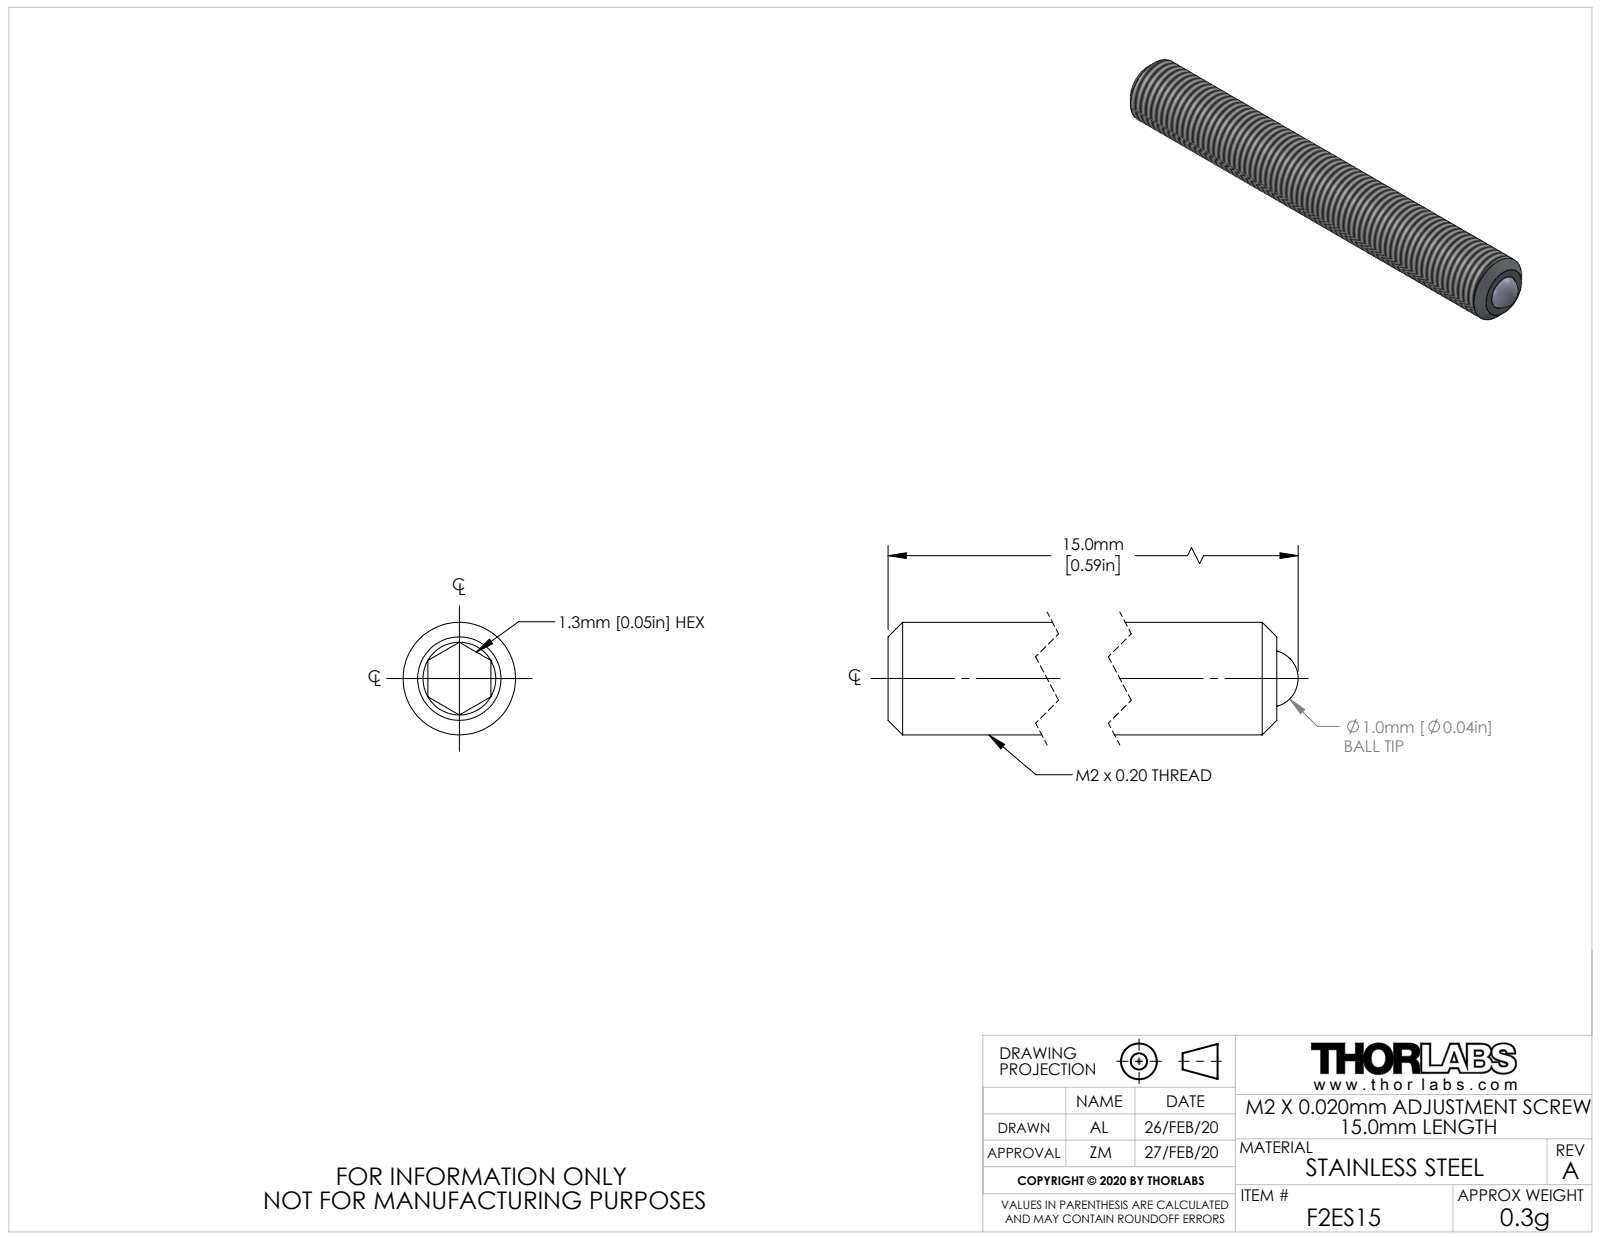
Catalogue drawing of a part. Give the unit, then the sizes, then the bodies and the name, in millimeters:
Units: millimetres
Overall size (bounding box): 15 × 2 × 2
Round holes (diameter × count): ⌀1 ×1
Round bosses / shafts (diameter × count): ⌀2 ×1
Main face-to-face distances: 1.1, 12.6, 2, 14.6
Volume: 50 mm³ · Surface area: 106 mm²
Bodies: 2 solids, 28 faces (9 planar, 4 cylindrical, 15 other)
Part name (STEP PRODUCT): TTN210093-E0W
STEP written by: SolidWorks 2018 (AUTOMOTIVE_DESIGN)
